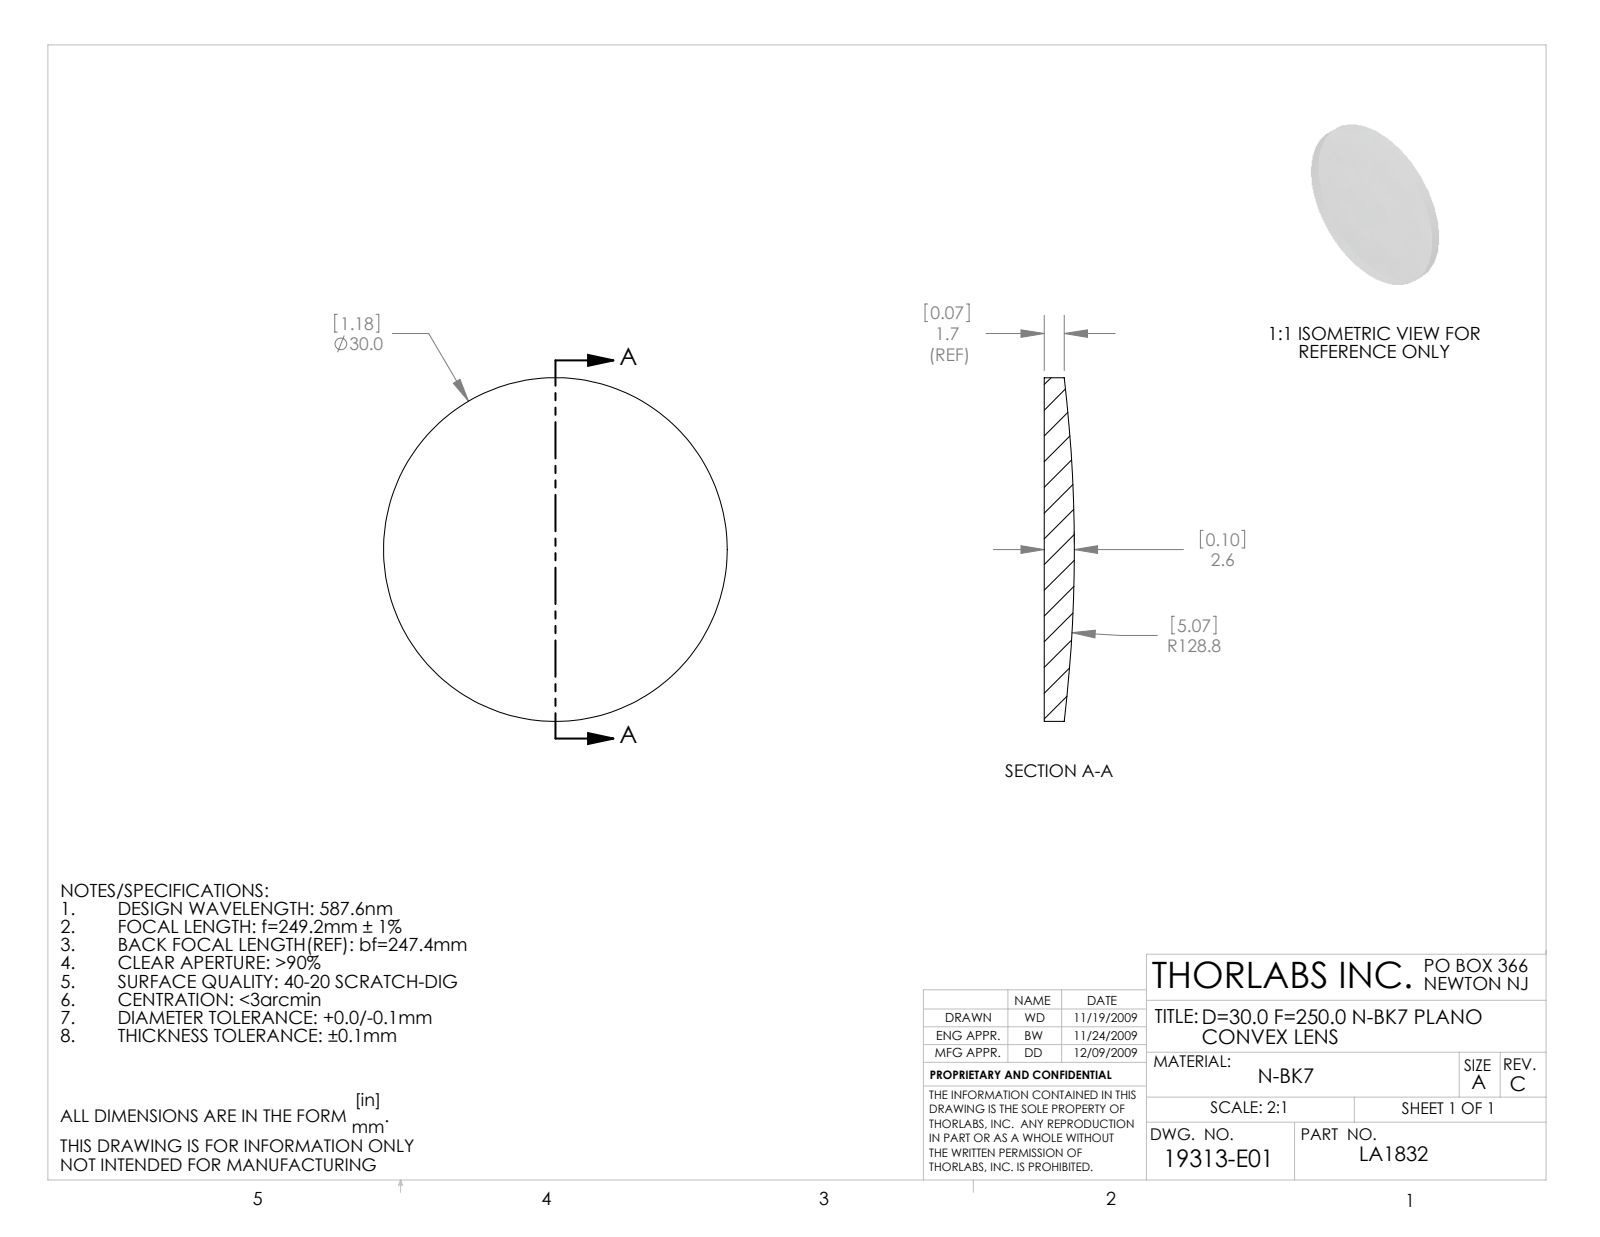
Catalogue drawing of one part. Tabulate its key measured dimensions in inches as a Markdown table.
| quantity | value |
| --- | --- |
| part name | 19313-E0W |
| STEP written by | SolidWorks 2009 (AUTOMOTIVE_DESIGN) |
| units | inches |
| bodies | 1 solid, 5 faces (1 planar, 2 cylindrical, 2 other) |
| overall size | 1.181 × 1.181 × 0.103 |
| volume | 0.094 in³ |
| surface area | 2.449 in² |
| round bosses / shafts (diameter × count) | 1.181 × 1 |
